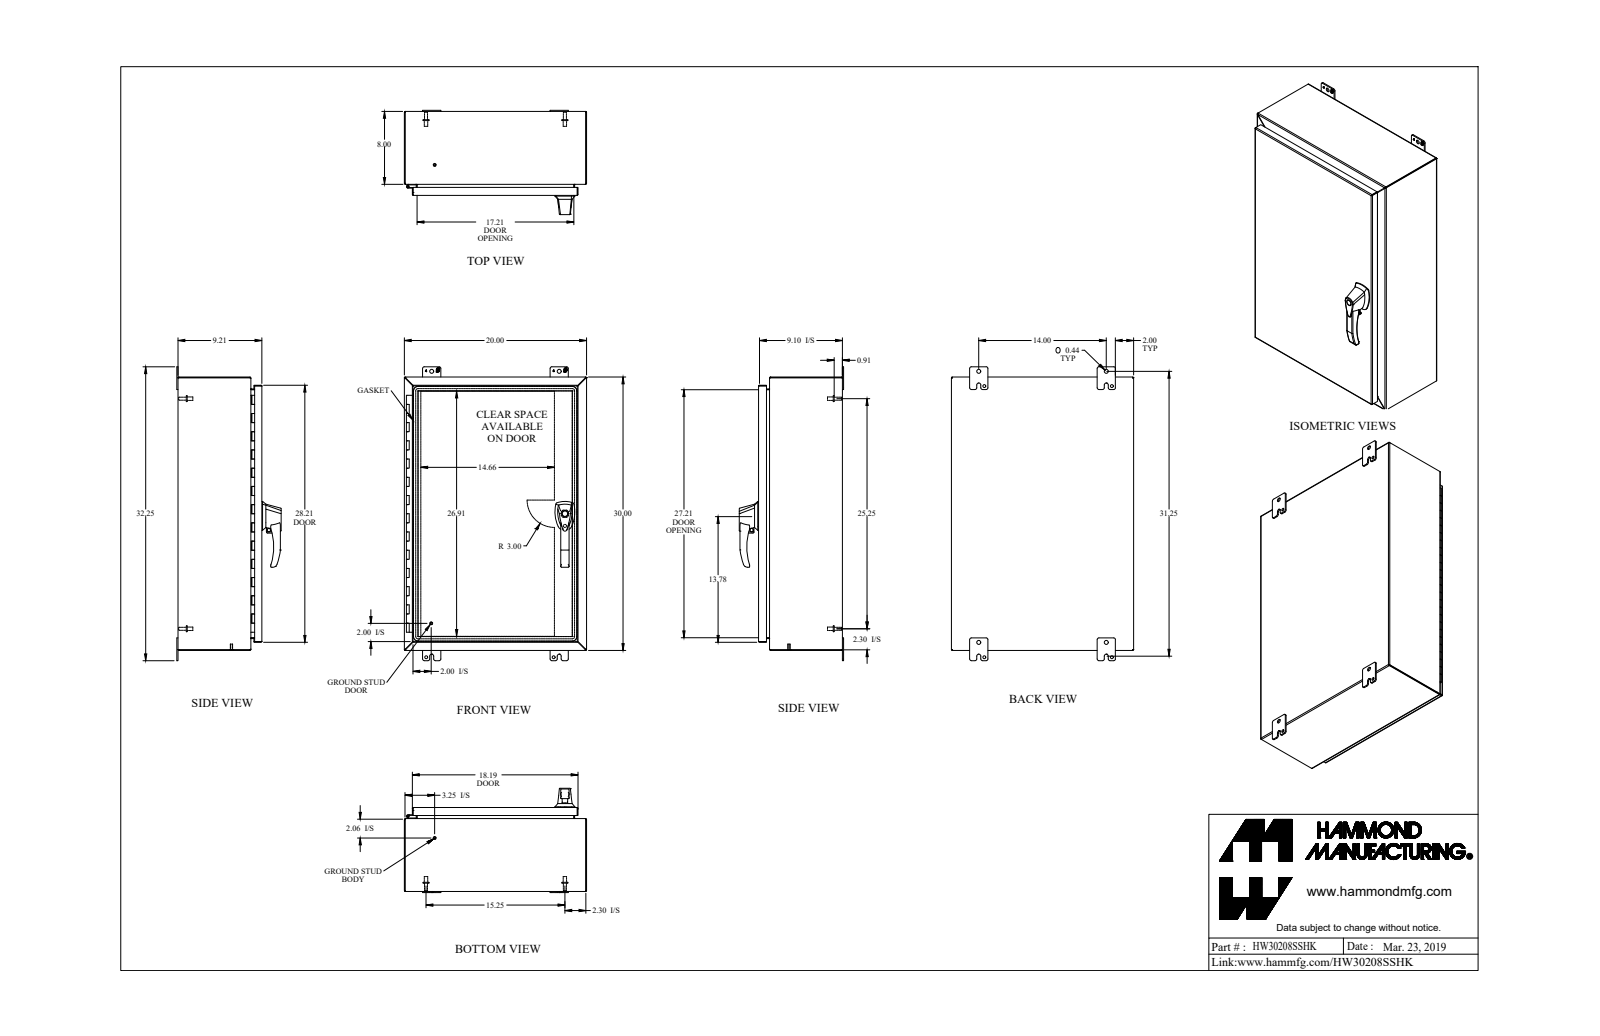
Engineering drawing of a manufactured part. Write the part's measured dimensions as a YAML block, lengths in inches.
part_name: "HW30208SSHK"
step_written_by: "SolidWorks 2018 (AUTOMOTIVE_DESIGN)"
units: inches
bodies: {solids: 42, faces: 1476, planar: 723, cylindrical: 599, other: 154}
overall_size: [32.25, 20, 11.45]
volume: 195
surface_area: 5012
round_holes:
  - {diameter: 0.176, count: 6}
  - {diameter: 0.313, count: 5}
  - {diameter: 0.25, count: 3}
  - {diameter: 0.265, count: 3}
  - {diameter: 0.413, count: 3}
  - {diameter: 0.196, count: 2}
  - {diameter: 0.256, count: 2}
  - {diameter: 0.394, count: 2}
  - {diameter: 0.437, count: 2}
  - {diameter: 0.187, count: 1}
  - {diameter: 0.233, count: 1}
  - {diameter: 0.33, count: 1}
round_bosses_or_shafts:
  - {diameter: 0.375, count: 9}
  - {diameter: 0.25, count: 7}
  - {diameter: 0.156, count: 6}
  - {diameter: 0.65, count: 4}
  - {diameter: 0.332, count: 4}
  - {diameter: 0.313, count: 4}
  - {diameter: 1, count: 3}
  - {diameter: 0.51, count: 3}
partial_cylinders:
  - {radius: 0.25, count: 27}
  - {radius: 0.188, count: 24}
  - {radius: 0.036, count: 20}
  - {radius: 0.108, count: 20}
  - {radius: 0.06, count: 12}
  - {radius: 0.125, count: 9}
  - {radius: 0.045, count: 8}
  - {radius: 0.218, count: 8}
face_to_face_distances: [0.072, 0.072, 9.138, 9.066, 9.138, 9.21, 19.928, 29.928, 7.928, 19.856]
hole_center_spacings: [1.111, 11.118, 11.119, 22.237, 1.338, 9.78, 10.563, 10.565]
